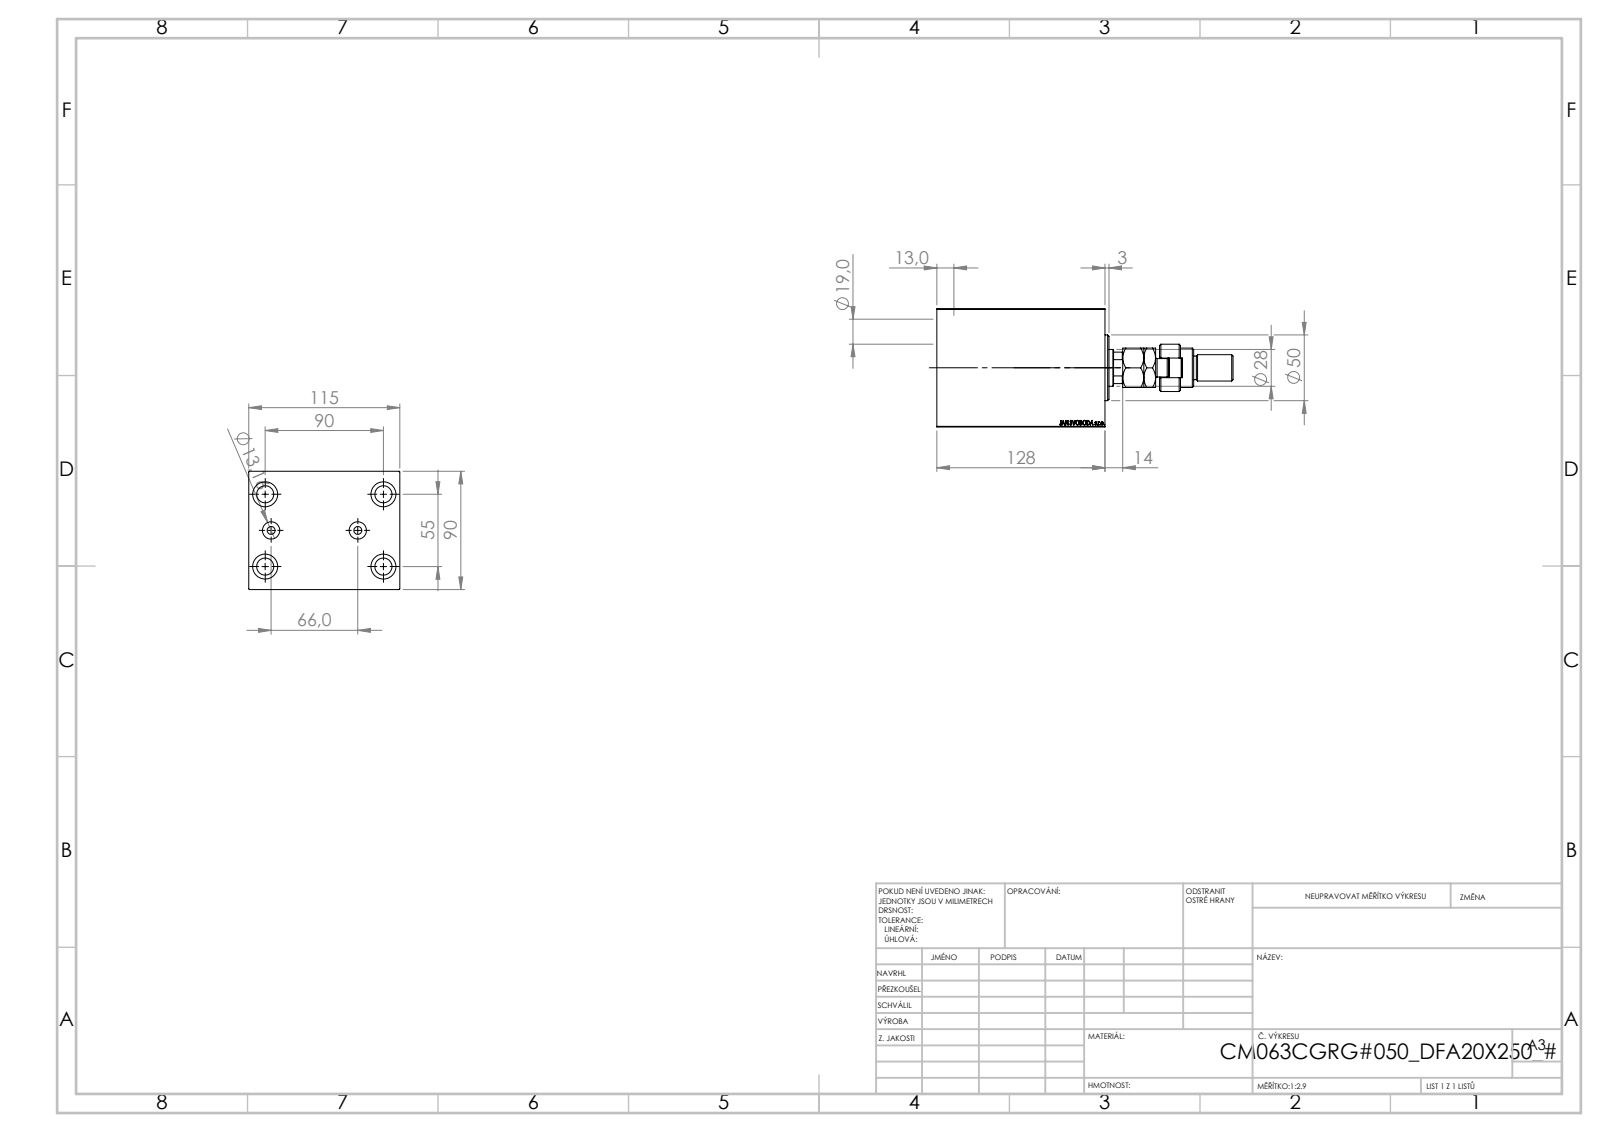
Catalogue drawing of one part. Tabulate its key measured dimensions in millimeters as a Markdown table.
| quantity | value |
| --- | --- |
| part name | V450CM_C_Body; FEMALE_PART_FOR_DFA; V450CM_VC_B; V450CM_C_VCP (+1 more) |
| STEP written by | SolidWorks 2019 (CONFIG_CONTROL_DESIGN) |
| units | millimeters |
| bodies | 5 solids, 946 faces (437 planar, 71 cylindrical, 438 other) |
| overall size | 225.5 × 115 × 90 |
| volume | 1 161 000 mm³ |
| surface area | 155 876 mm² |
| round holes (diameter × count) | 13 × 4, 19 × 4, 6 × 2, 13.16 × 2, 18.5 × 1, 28 × 1, 31.5 × 1, 63 × 1, 65 × 1, 72 × 1 |
| round bosses / shafts (diameter × count) | 50 × 1, 36 × 1, 30 × 1, 22 × 1, 20 × 1, 18 × 1, 14 × 1 |
| partial cylindrical surfaces (radius × count) | 7.5 × 1, 12 × 1, 13.5 × 1 |
| main face-to-face distances | 90, 115, 128, 48.5, 79.5, 118, 10, 60, 69.5, 5 |
| hole center spacings | 30, 52.74, 82.71, 33, 55, 90, 105.48, 66 |
